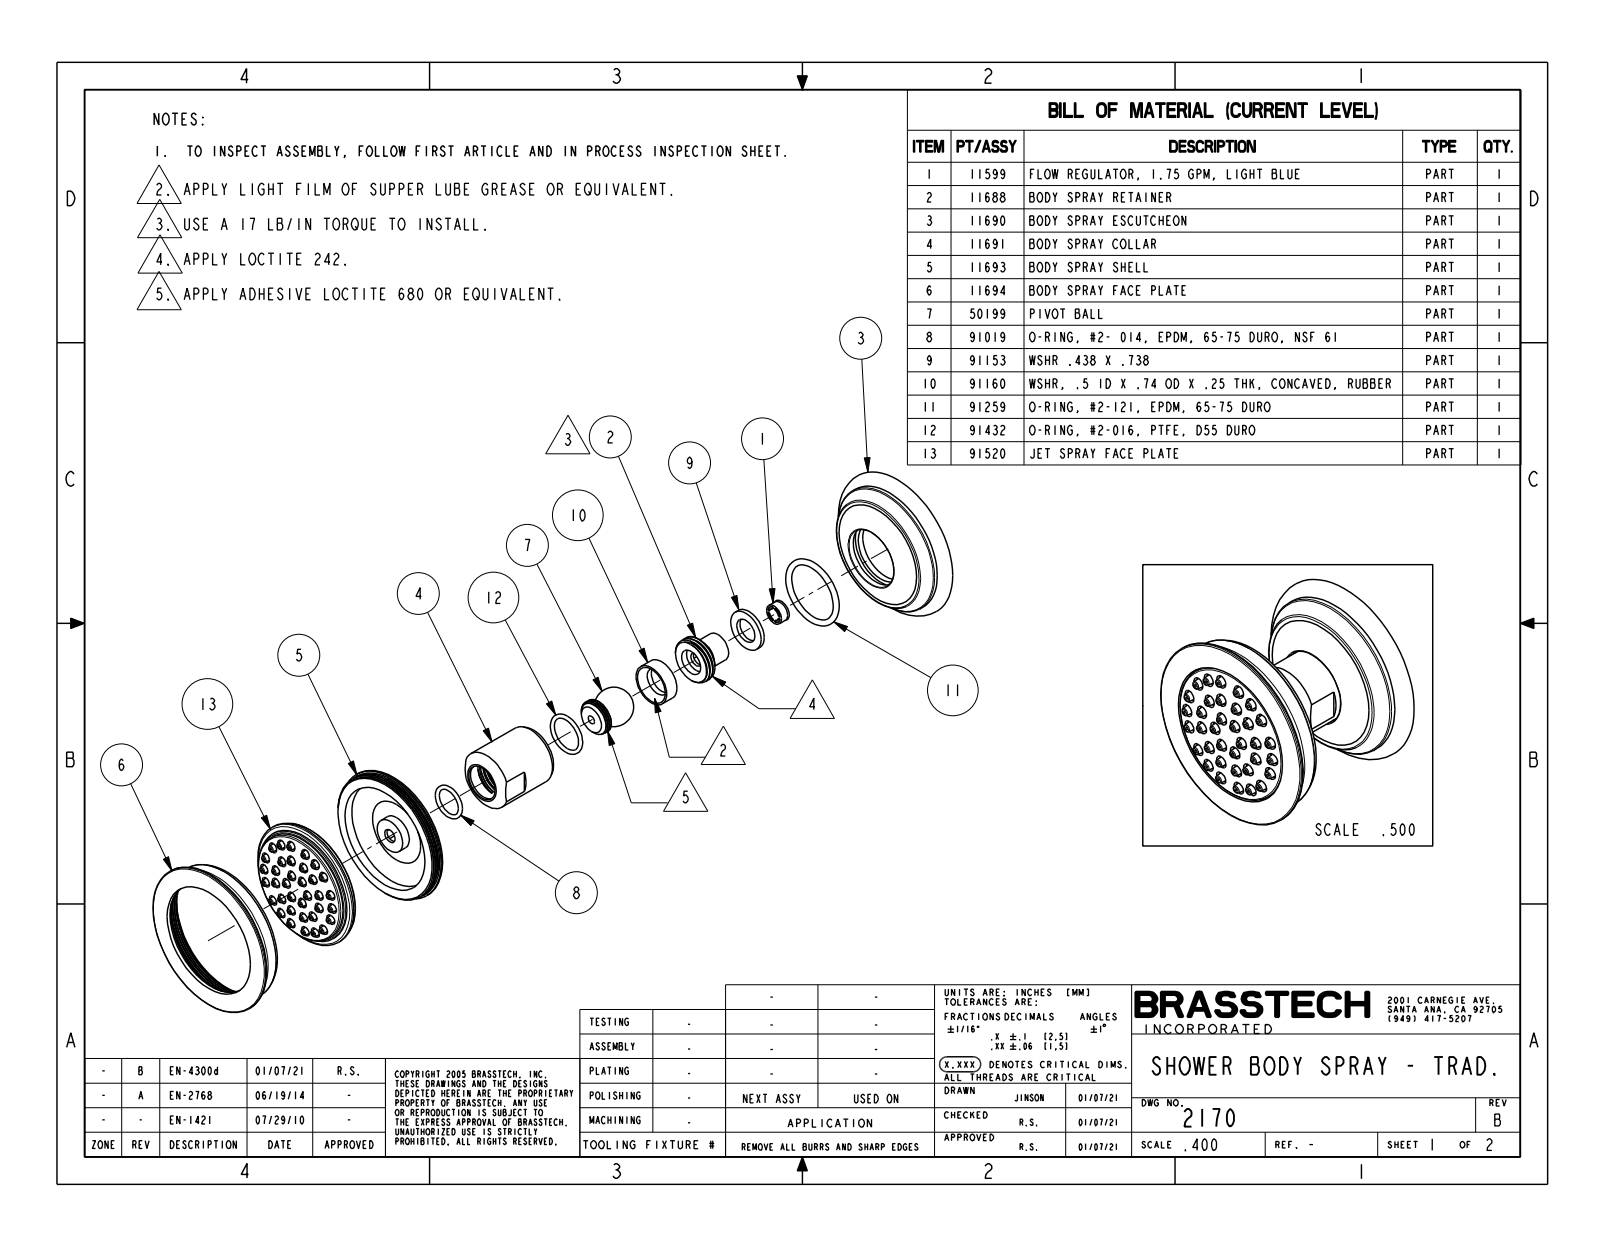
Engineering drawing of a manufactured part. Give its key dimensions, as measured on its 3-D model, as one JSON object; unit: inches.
{"part_name": "2170", "step_written_by": "CREO PARAMETRIC BY PTC INC, 2018400 (CONFIG_CONTROL_DESIGN)", "units": "inches", "bodies": {"solids": 1, "faces": 595, "planar": 176, "cylindrical": 155, "other": 264}, "overall_size": [2.726, 2.726, 2.317], "volume_in3": 5.687, "surface_area_in2": 34.92, "round_holes": [[0.039, 36], [0.181, 31], [1.092, 1], [2.022, 1]], "round_bosses_or_shafts": [[2.726, 1], [2.524, 1], [2.336, 1], [1.992, 1], [1.062, 1], [0.315, 1]], "partial_cylinders_radius": [[0.091, 5]], "face_to_face_distances": [2.219, 1.39, 0.829, 0.47, 0.92, 1.749, 1.785, 1.315, 0.395, 0.434], "hole_center_spacings": [0.827, 1.432, 0.541, 0.593, 1.285, 1.544, 1.041, 1.106]}
